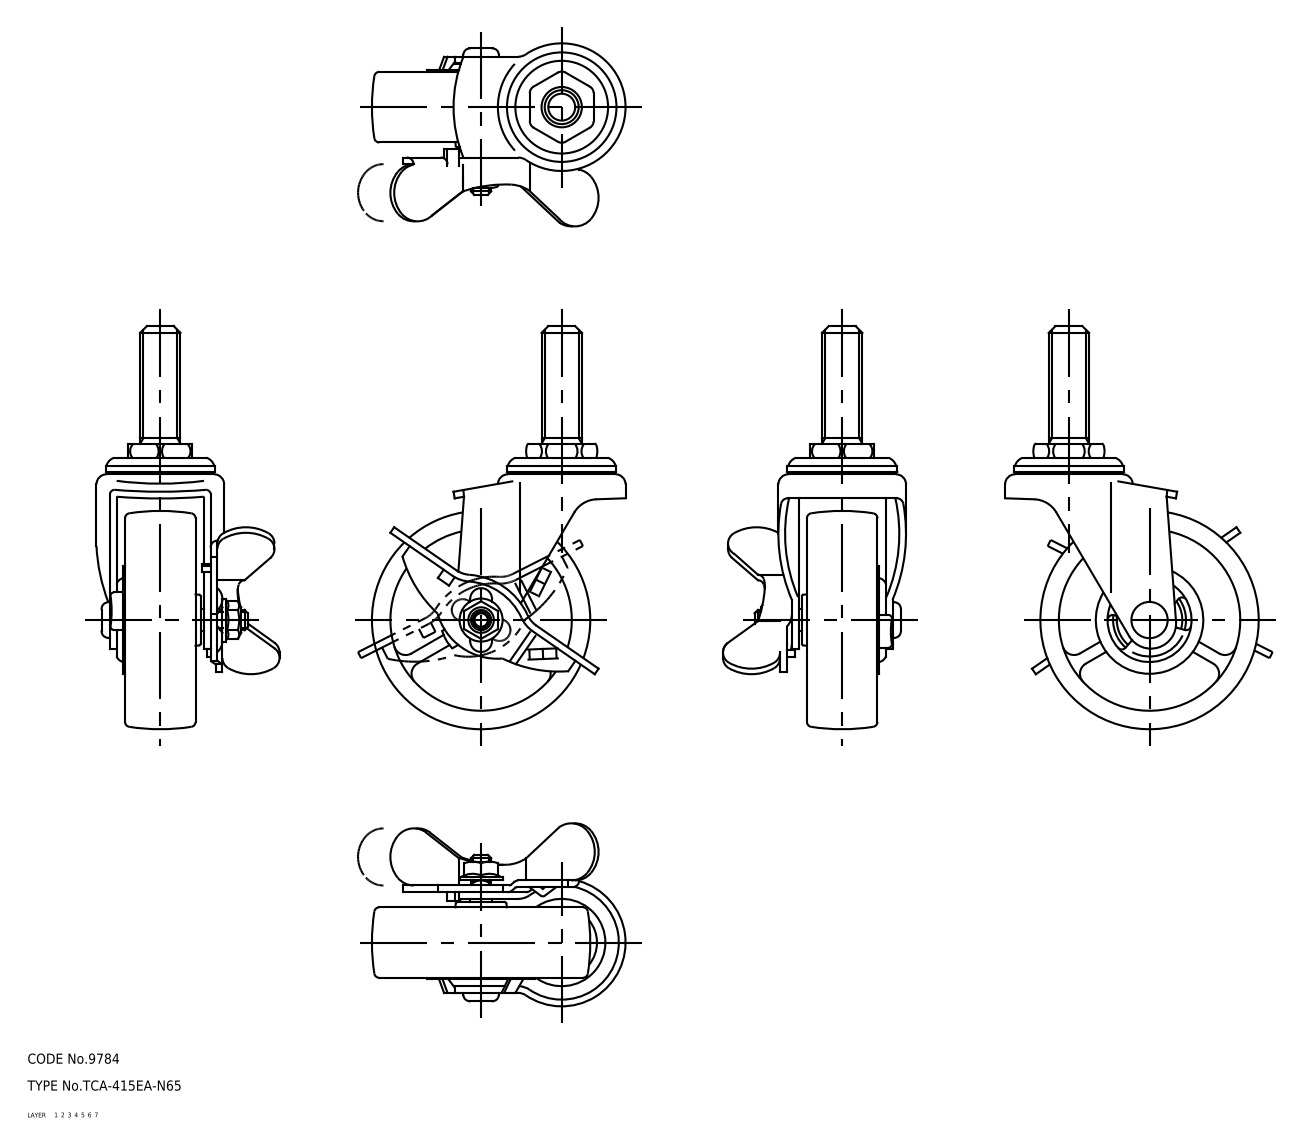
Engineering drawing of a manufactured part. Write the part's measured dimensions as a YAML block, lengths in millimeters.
part_name: "67153692; 67153705; 67153718; 67153731 (+2 more)"
step_written_by: "CADfix (AUTOMOTIVE_DESIGN)"
units: millimeters
bodies: {solids: 6, faces: 493, planar: 0, cylindrical: 0, other: 493}
overall_size: [120, 75.5, 54.49]
volume: 73272
surface_area: 34844
